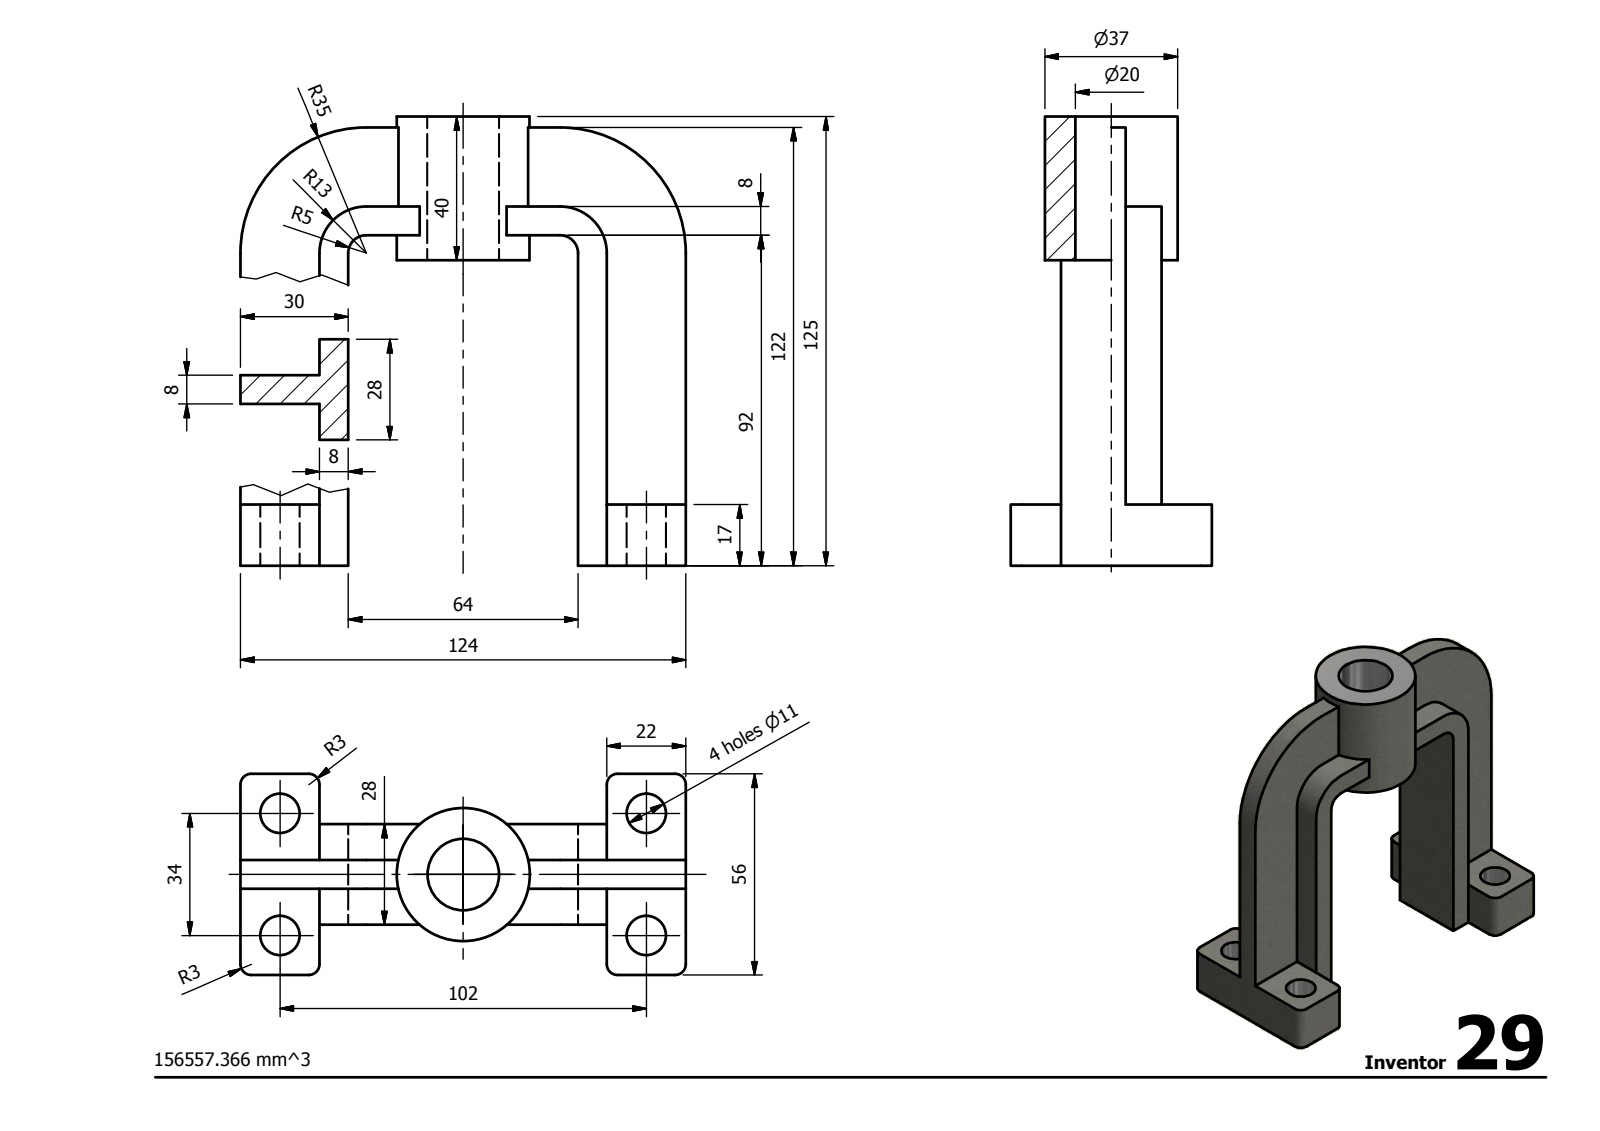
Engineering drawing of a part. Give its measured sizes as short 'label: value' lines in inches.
written by: Autodesk Inventor 2014 (AUTOMOTIVE_DESIGN)
unit: in
bodies: 1 solid, 62 faces (40 planar, 22 cylindrical, 0 other)
size: 4.921 × 4.882 × 2.205
volume: 9.554 in³; area: 69.22 in²
holes: 4× ⌀0.433, 1× ⌀0.787
bosses: 1× ⌀1.457
rounds: 8× R0.118, 2× R0.197, 2× R0.512, 2× R1.378
face distances: 0.315, 0.394, 0.709, 2.835, 1.181, 0.866, 3.701, 4.016, 2.52, 1.102
hole spacings: 2.117, 1.339, 4.016, 4.233
